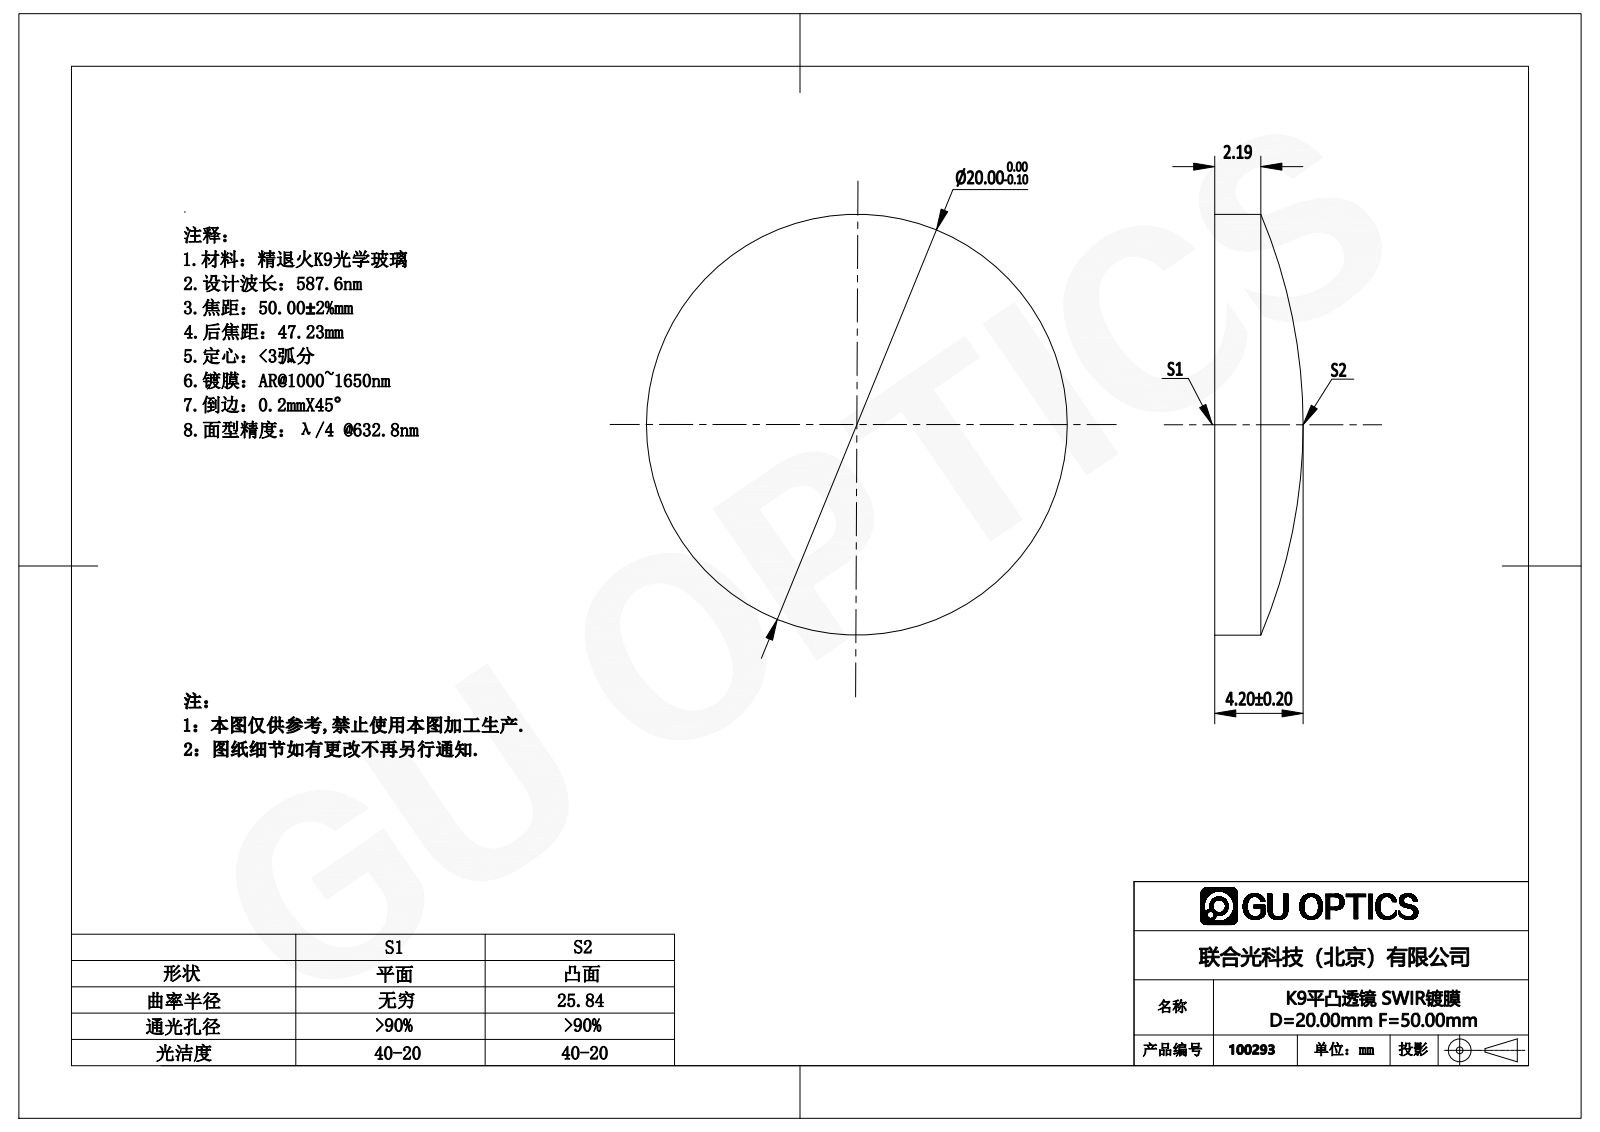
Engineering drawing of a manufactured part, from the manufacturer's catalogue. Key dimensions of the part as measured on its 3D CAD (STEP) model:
Part name (STEP PRODUCT): 100121
STEP written by: SolidWorks 2016 (AUTOMOTIVE_DESIGN)
Units: millimetres
Bodies: 1 solid, 5 faces (1 planar, 2 cylindrical, 2 other)
Overall size (bounding box): 20 × 20 × 4.2
Volume: 1 008 mm³ · Surface area: 779 mm²
Round bosses / shafts (diameter × count): ⌀20 ×1
